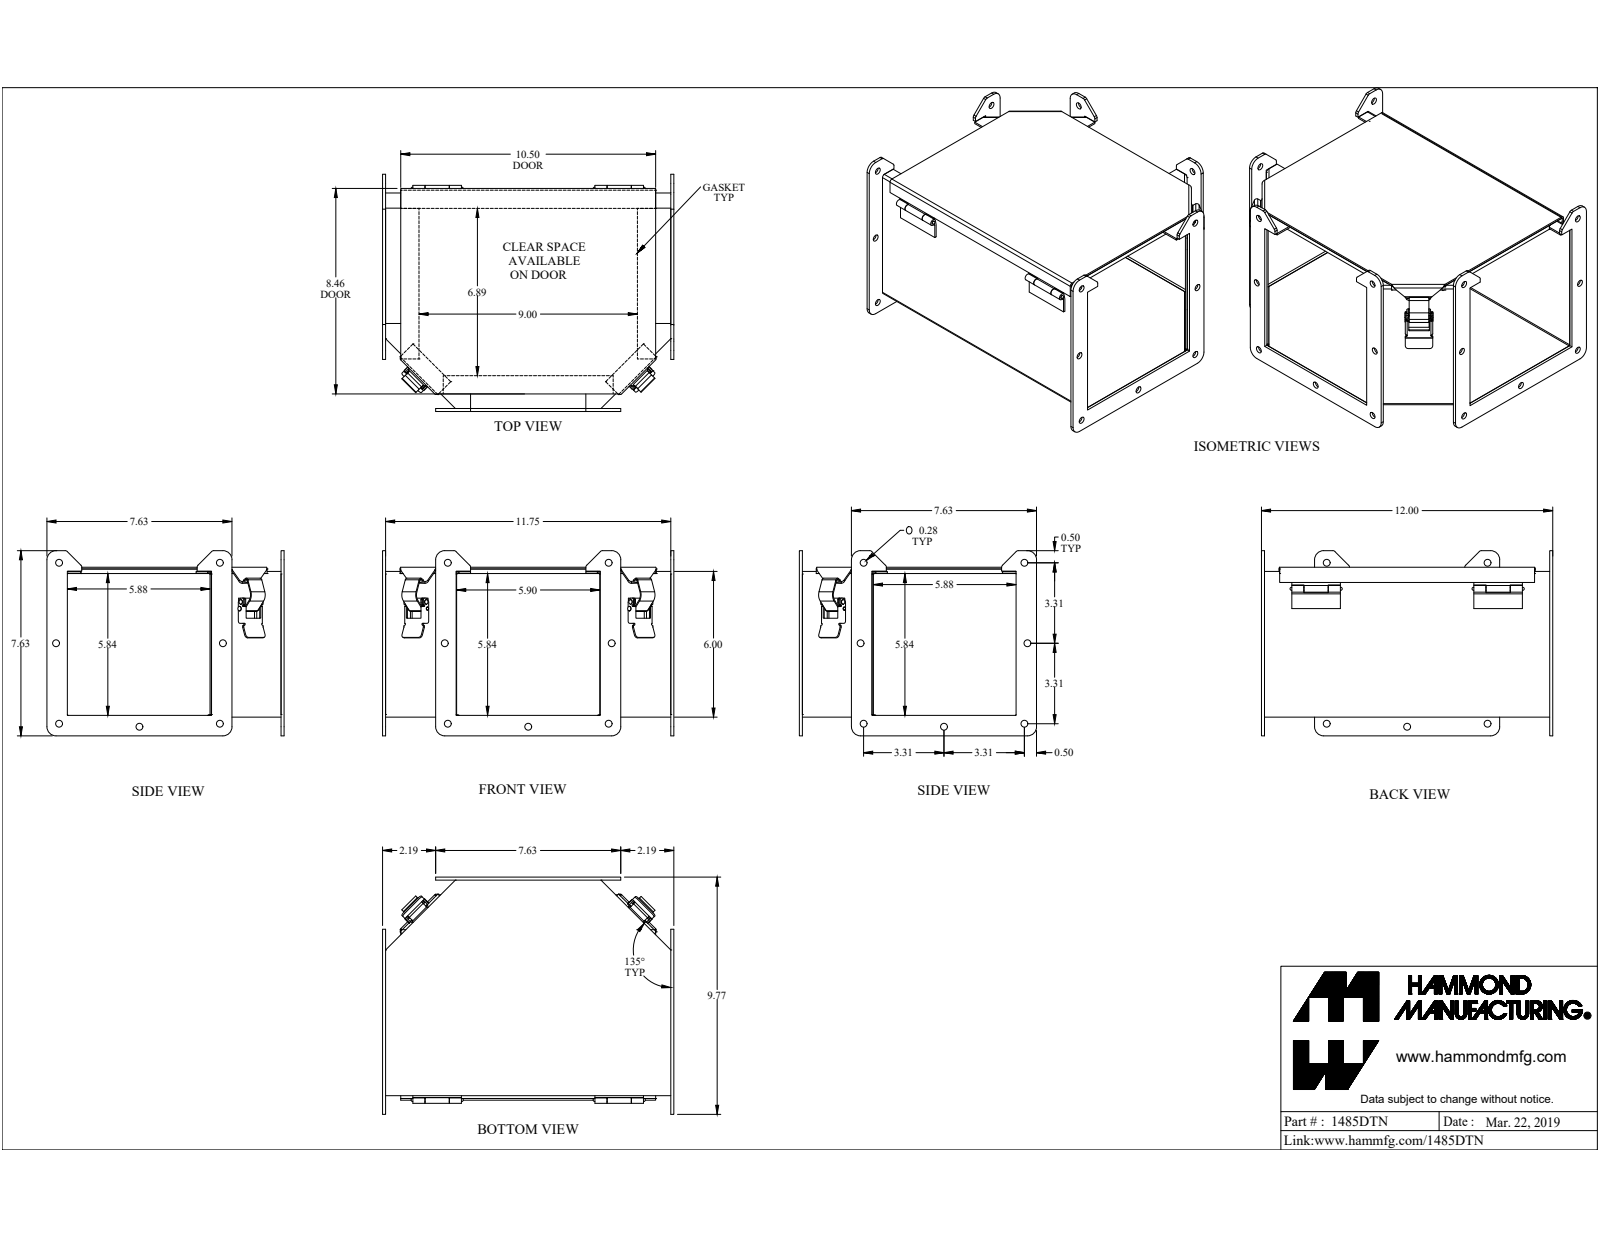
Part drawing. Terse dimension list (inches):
name: 1485DTN
written by: SolidWorks 2019 (CONFIG_CONTROL_DESIGN)
unit: in
bodies: 23 solids, 535 faces (322 planar, 185 cylindrical, 28 other)
size: 12 × 9.771 × 7.625
volume: 35.96 in³; area: 888.4 in²
holes: 14× ⌀0.281, 4× ⌀0.13, 4× ⌀0.164, 1× ⌀0.125
bosses: 6× ⌀0.187, 4× ⌀0.156, 2× ⌀0.125, 1× ⌀0.275, 1× ⌀0.125
rounds: 16× R0.125, 14× R0.016, 11× R0.036, 11× R0.108, 8× R0.035, 8× R0.039, 8× R0.375, 6× R0.076
face distances: 0.072, 6.1, 6.028, 6.172, 0.072, 0.125, 11.875, 0.172, 5.928, 0.259
hole spacings: 7.519, 3.315, 6.625, 3.315, 0.285, 0.285, 4.861, 6.625
